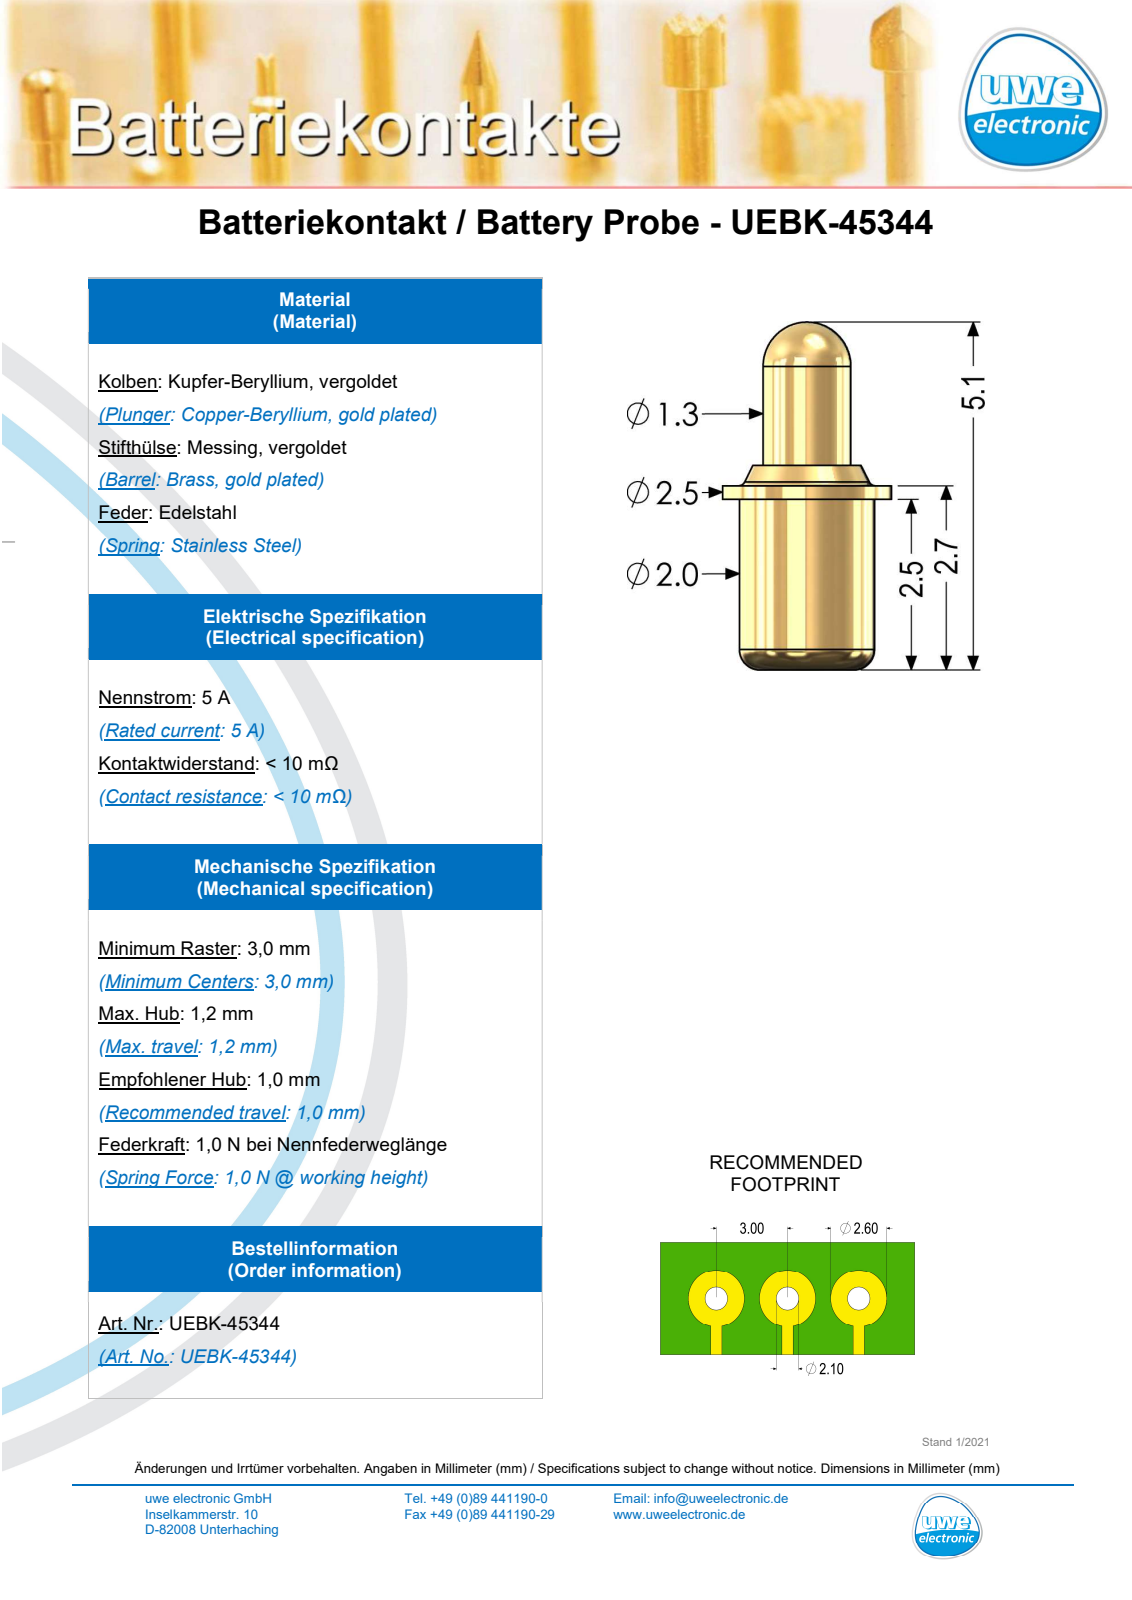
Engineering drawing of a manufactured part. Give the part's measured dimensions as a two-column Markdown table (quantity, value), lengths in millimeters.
| quantity | value |
| --- | --- |
| part name | UEBK-45344 |
| STEP written by | SolidWorks 2019 (AUTOMOTIVE_DESIGN) |
| units | millimeters |
| bodies | 1 solid, 18 faces (4 planar, 6 cylindrical, 8 other) |
| overall size | 5.1 × 2.5 × 2.5 |
| volume | 12 mm³ |
| surface area | 34 mm² |
| round bosses / shafts (diameter × count) | 2.5 × 1, 2 × 1, 1.3 × 1 |
| main face-to-face distances | 2.5, 2.7, 3, 0.5 |
